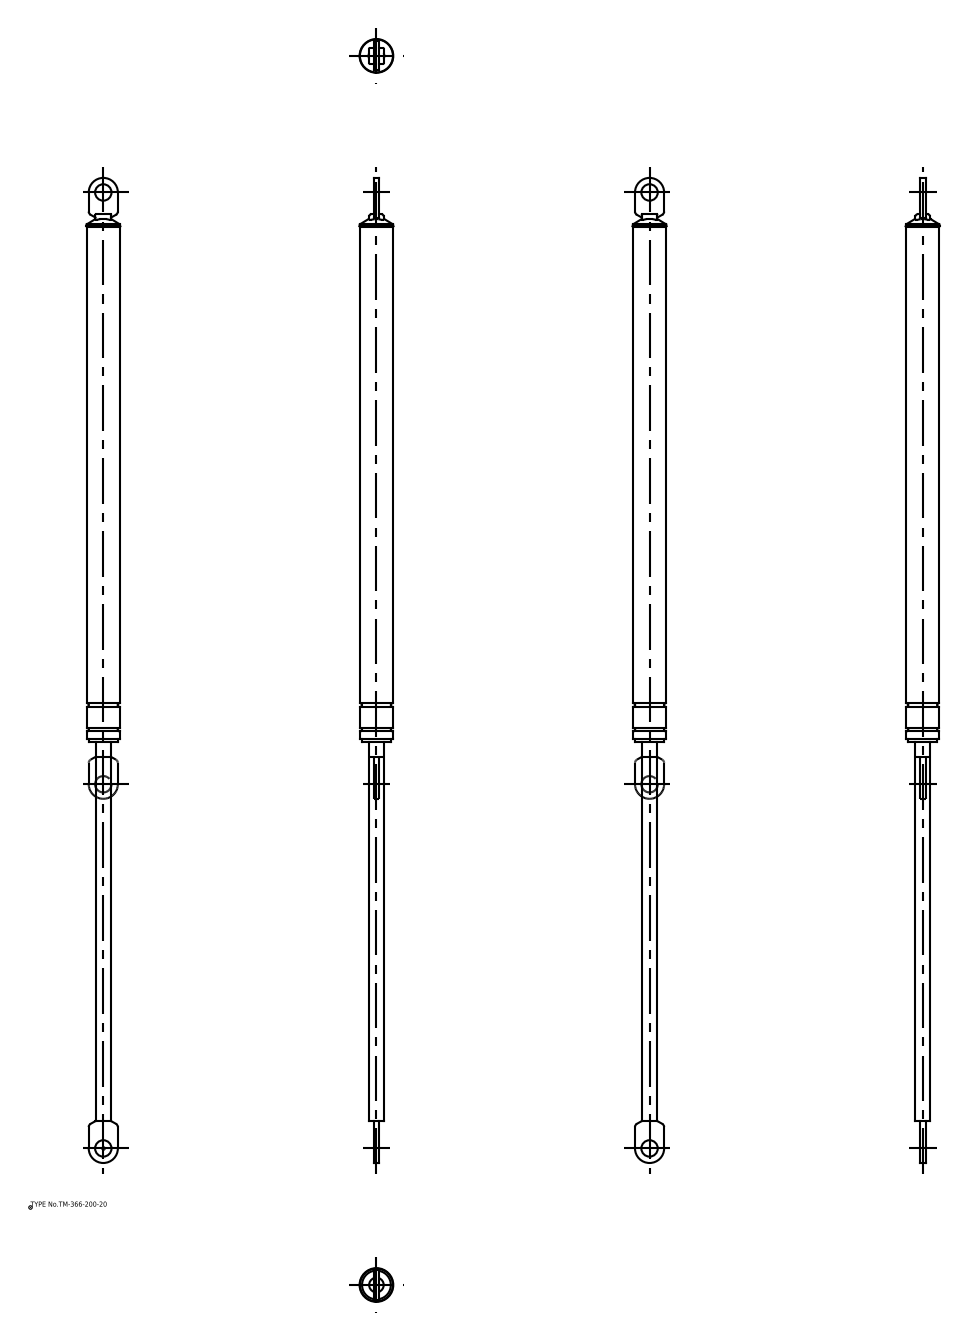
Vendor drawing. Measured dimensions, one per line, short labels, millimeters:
name: TM_366_200_20; TM_366_200_20_div
written by: spGate 16.7.1 (AUTOMOTIVE_DESIGN)
unit: mm
bodies: 2 solids, 89 faces (35 planar, 36 cylindrical, 18 other)
size: 541 × 18.5 × 18.5
volume: 84 810 mm³; area: 23 675 mm²
holes: 2× ⌀9
bosses: 1× ⌀18, 1× ⌀15.8, 1× ⌀8
rounds: 8× R0.3, 4× R2, 2× R0.5, 2× R1.15, 2× R8
face distances: 3.2, 16, 1.7, 208, 209.7, 3.7, 12.3, 13.5, 1.8, 2.4
hole spacings: 525
